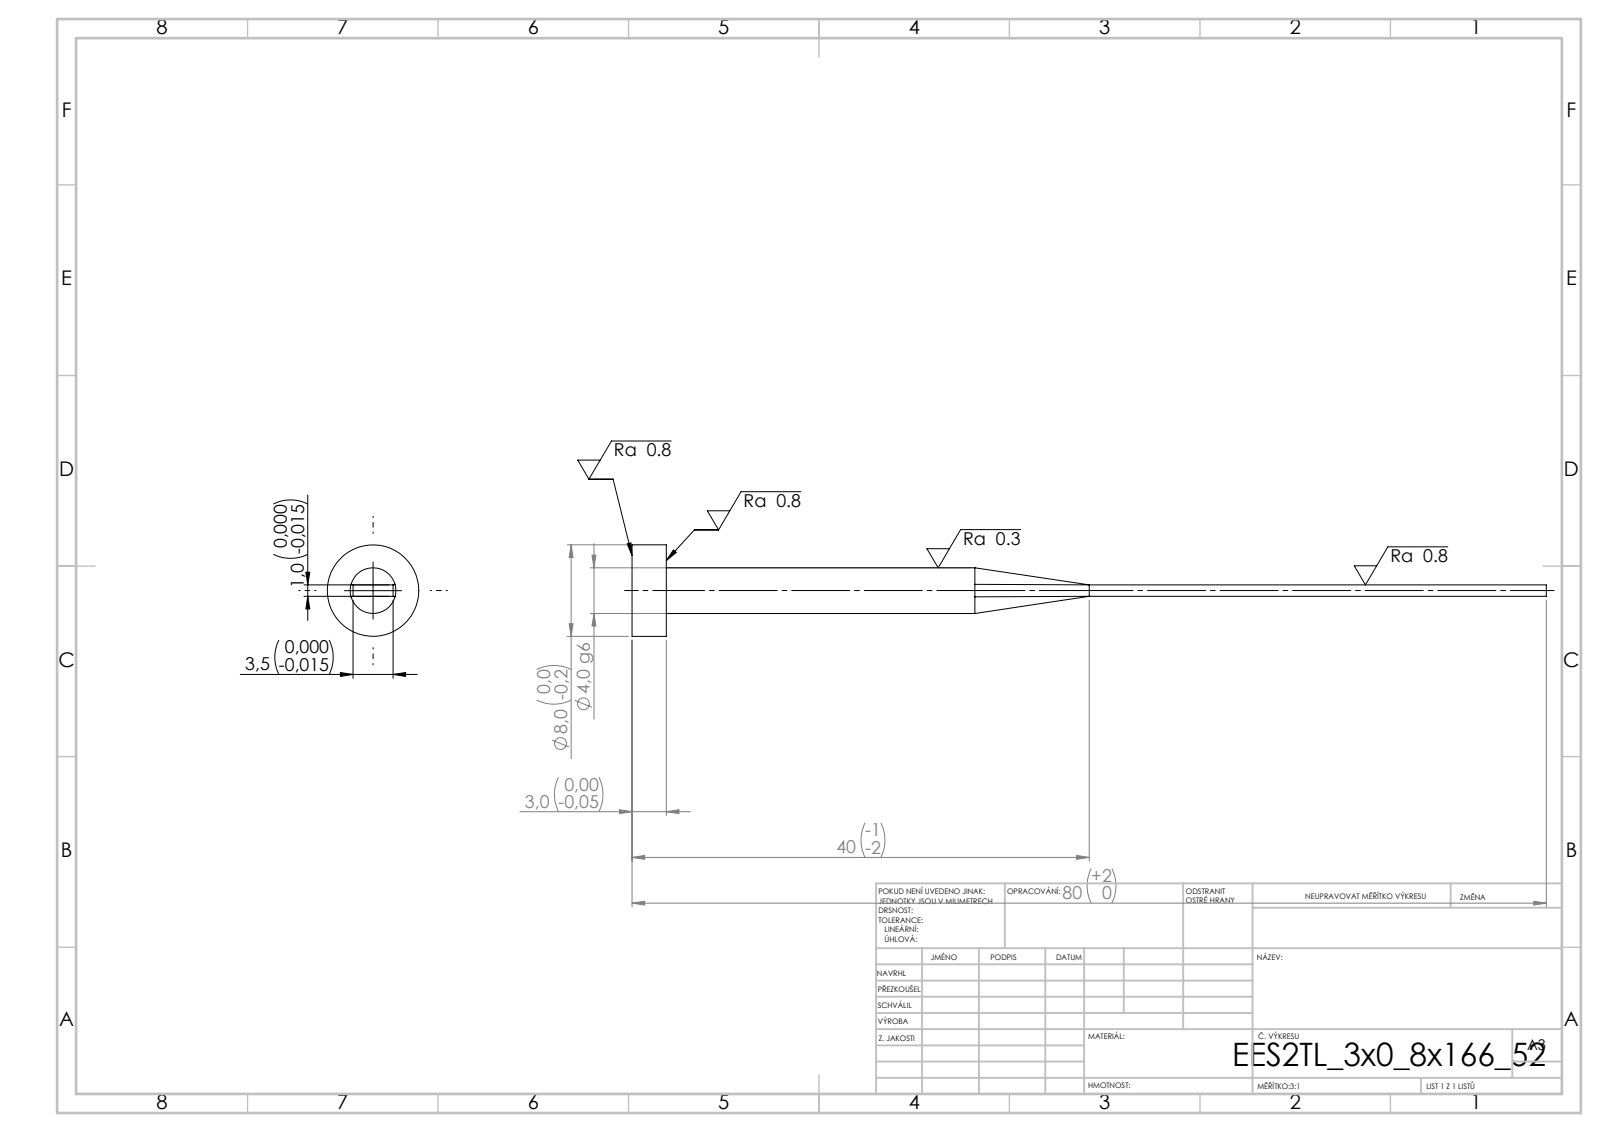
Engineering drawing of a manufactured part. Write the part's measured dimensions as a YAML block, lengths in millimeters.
step_written_by: "SolidWorks 2019 (CONFIG_CONTROL_DESIGN)"
units: millimeters
bodies: {solids: 1, faces: 15, planar: 7, cylindrical: 4, other: 4}
overall_size: [80, 8, 8]
volume: 707
surface_area: 970
round_bosses_or_shafts:
  - {diameter: 8, count: 1}
  - {diameter: 4, count: 1}
face_to_face_distances: [1, 3.5, 3, 80, 77]
